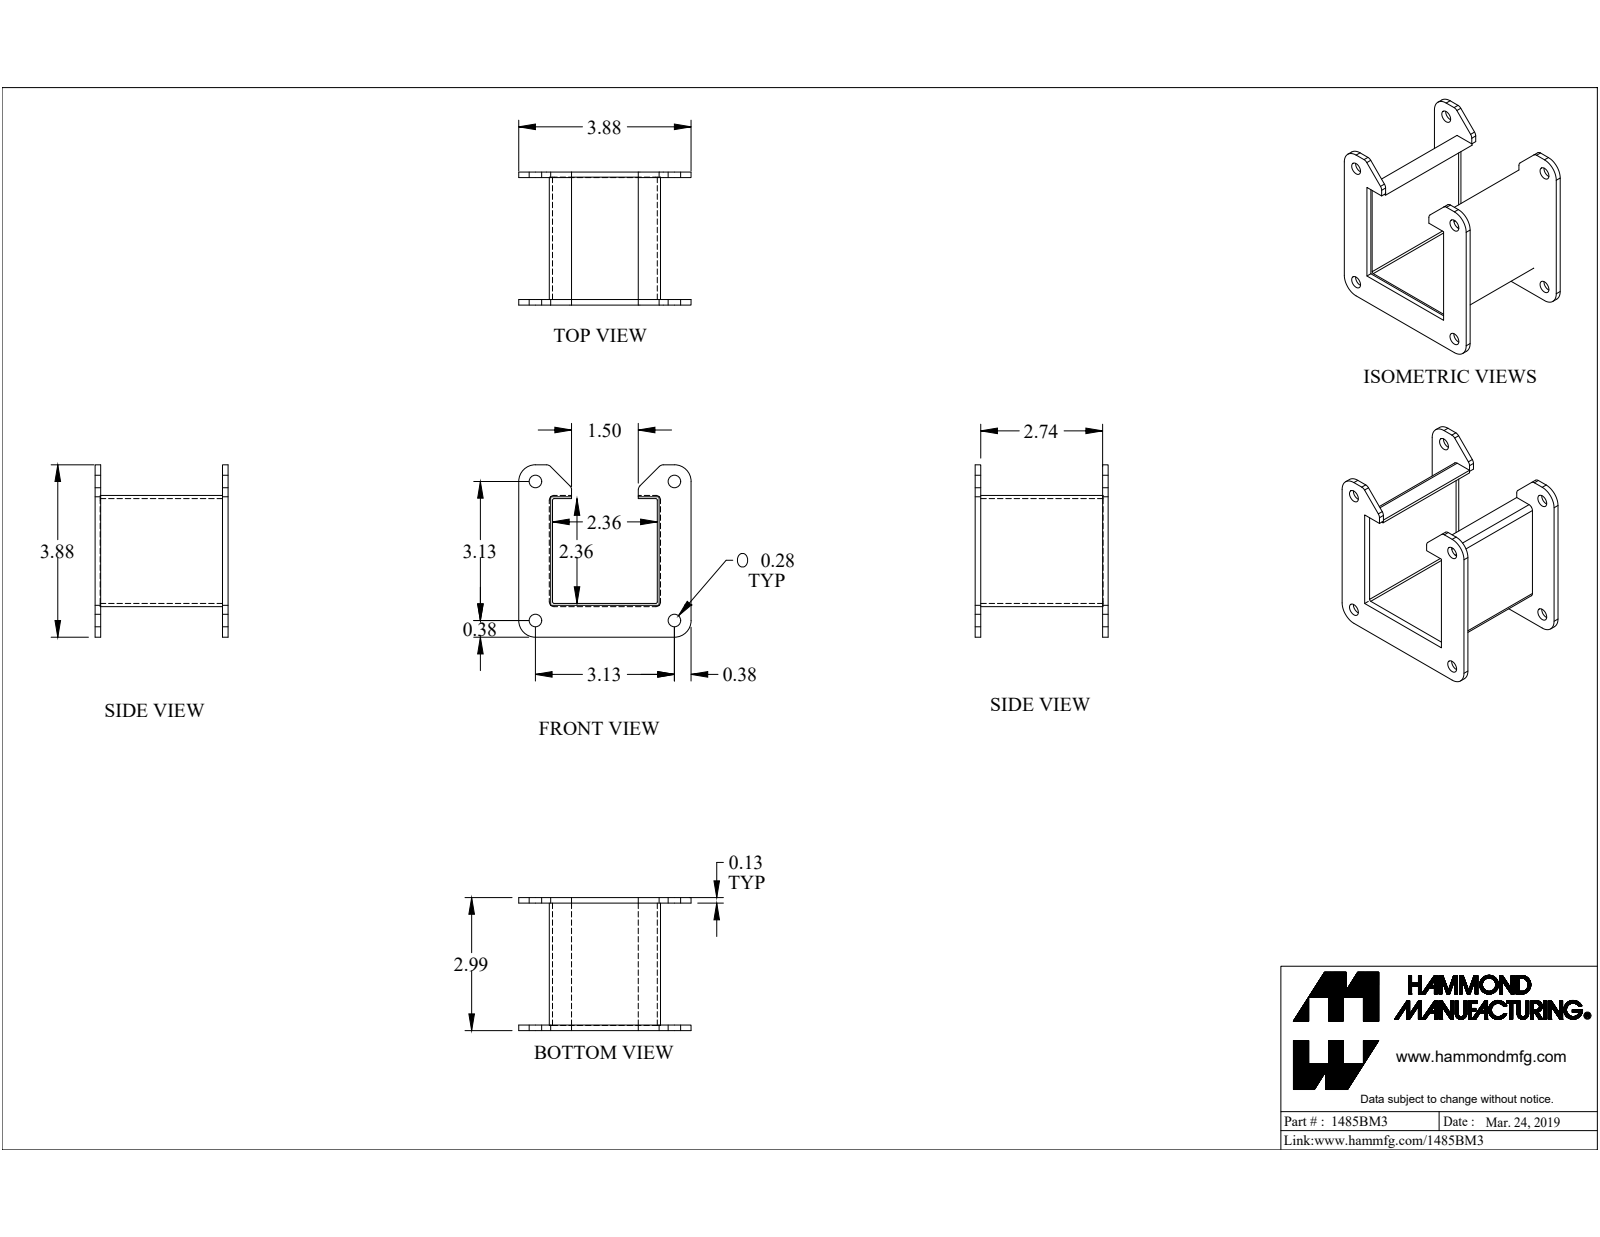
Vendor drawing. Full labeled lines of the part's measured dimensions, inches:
Part name (STEP PRODUCT): 1485BM3
STEP written by: SolidWorks 2019 (CONFIG_CONTROL_DESIGN)
Units: inches
Bodies: 3 solids, 78 faces (46 planar, 32 cylindrical, 0 other)
Overall size (bounding box): 3.875 × 3.875 × 2.99
Volume: 3.441 in³ · Surface area: 81.98 in²
Round holes (diameter × count): ⌀0.281 ×4
Partial cylindrical surfaces — rounded edges, fillets, slot ends (radius × count): R0.036 ×4, R0.108 ×4, R0.125 ×4, R0.375 ×4
Main face-to-face distances: 0.072, 2.428, 2.5, 2.356, 2.865, 0.125, 0.125, 2.74, 2.99, 2.865
Hole centre spacings: 3.125, 4.42
